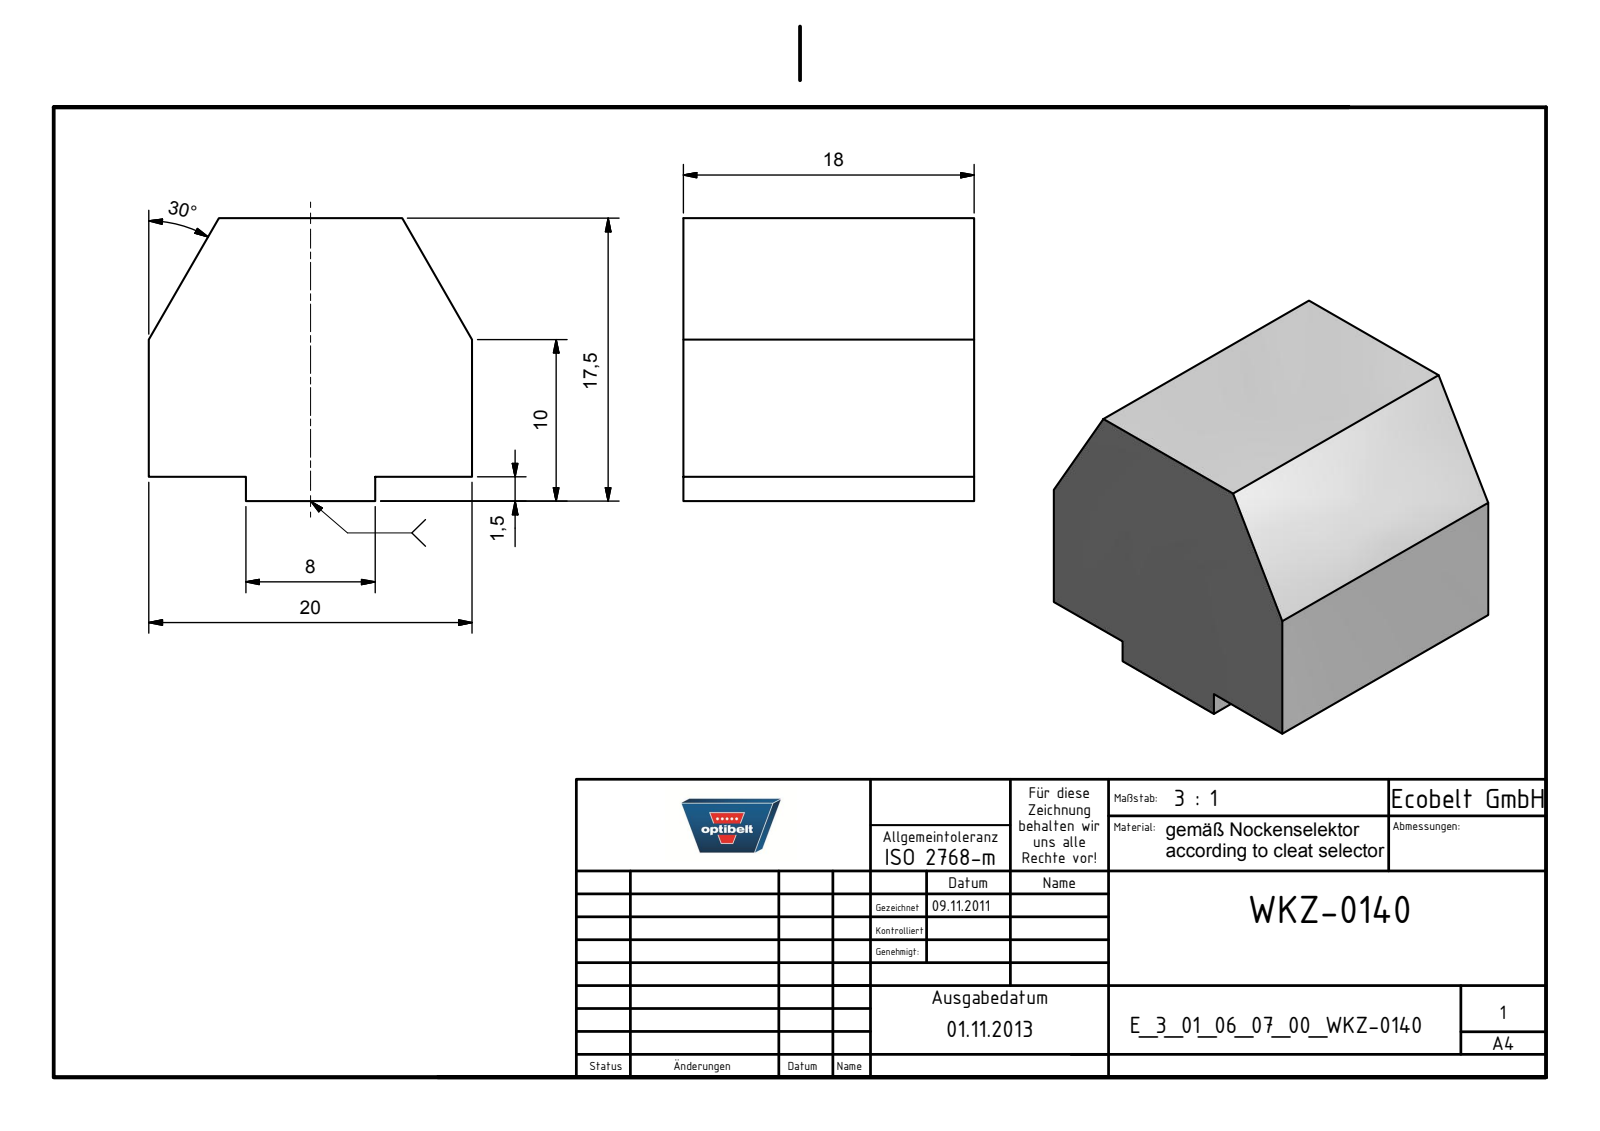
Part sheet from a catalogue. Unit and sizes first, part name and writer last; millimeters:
Units: millimetres
Overall size (bounding box): 20 × 18 × 17.5
Main face-to-face distances: 18, 16, 20, 1.5, 17.5, 6, 14, 8
Volume: 5 391 mm³ · Surface area: 1 835 mm²
Bodies: 1 solid, 12 faces (12 planar, 0 cylindrical, 0 other)
Part name (STEP PRODUCT): E_3_01_06_07_00_WKZ-0140
STEP written by: Autodesk Inventor 2025 (AUTOMOTIVE_DESIGN)
